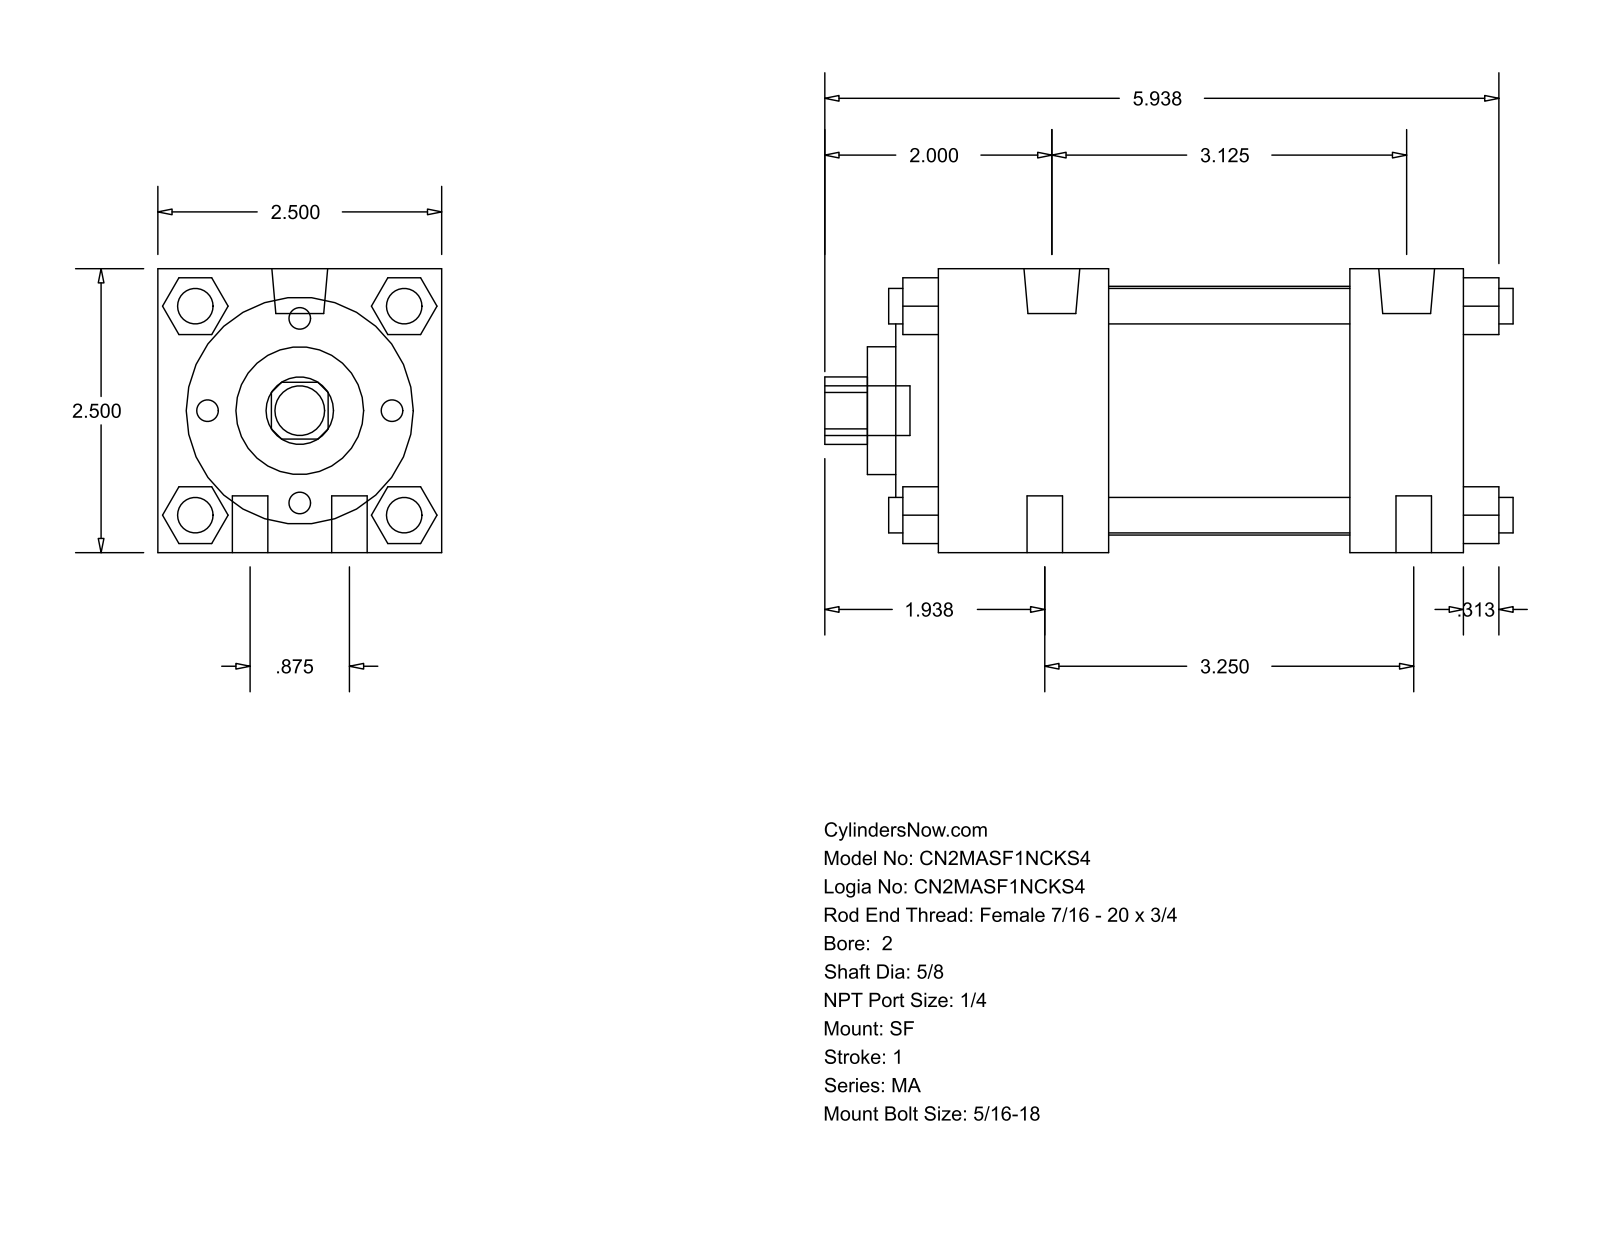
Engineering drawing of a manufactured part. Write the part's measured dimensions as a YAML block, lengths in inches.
part_name: "MA_SF__0200_0.625"
step_written_by: "GSSL Pune (CONFIG_CONTROL_DESIGN)"
units: inches
bodies: {solids: 0, faces: 126, planar: 95, cylindrical: 31, other: 0}
overall_size: [6.063, 2.5, 2.5]
round_holes:
  - {diameter: 0.625, count: 1}
  - {diameter: 1.125, count: 1}
  - {diameter: 2, count: 1}
  - {diameter: 2.19, count: 1}
round_bosses_or_shafts:
  - {diameter: 0.313, count: 10}
  - {diameter: 0.492, count: 2}
  - {diameter: 0.437, count: 1}
partial_cylinders:
  - {radius: 0.297, count: 1}
face_to_face_distances: [2.5, 2.125, 0.5, 1.5, 0.375, 4.625, 3.625, 1, 3.125, 1.875]
